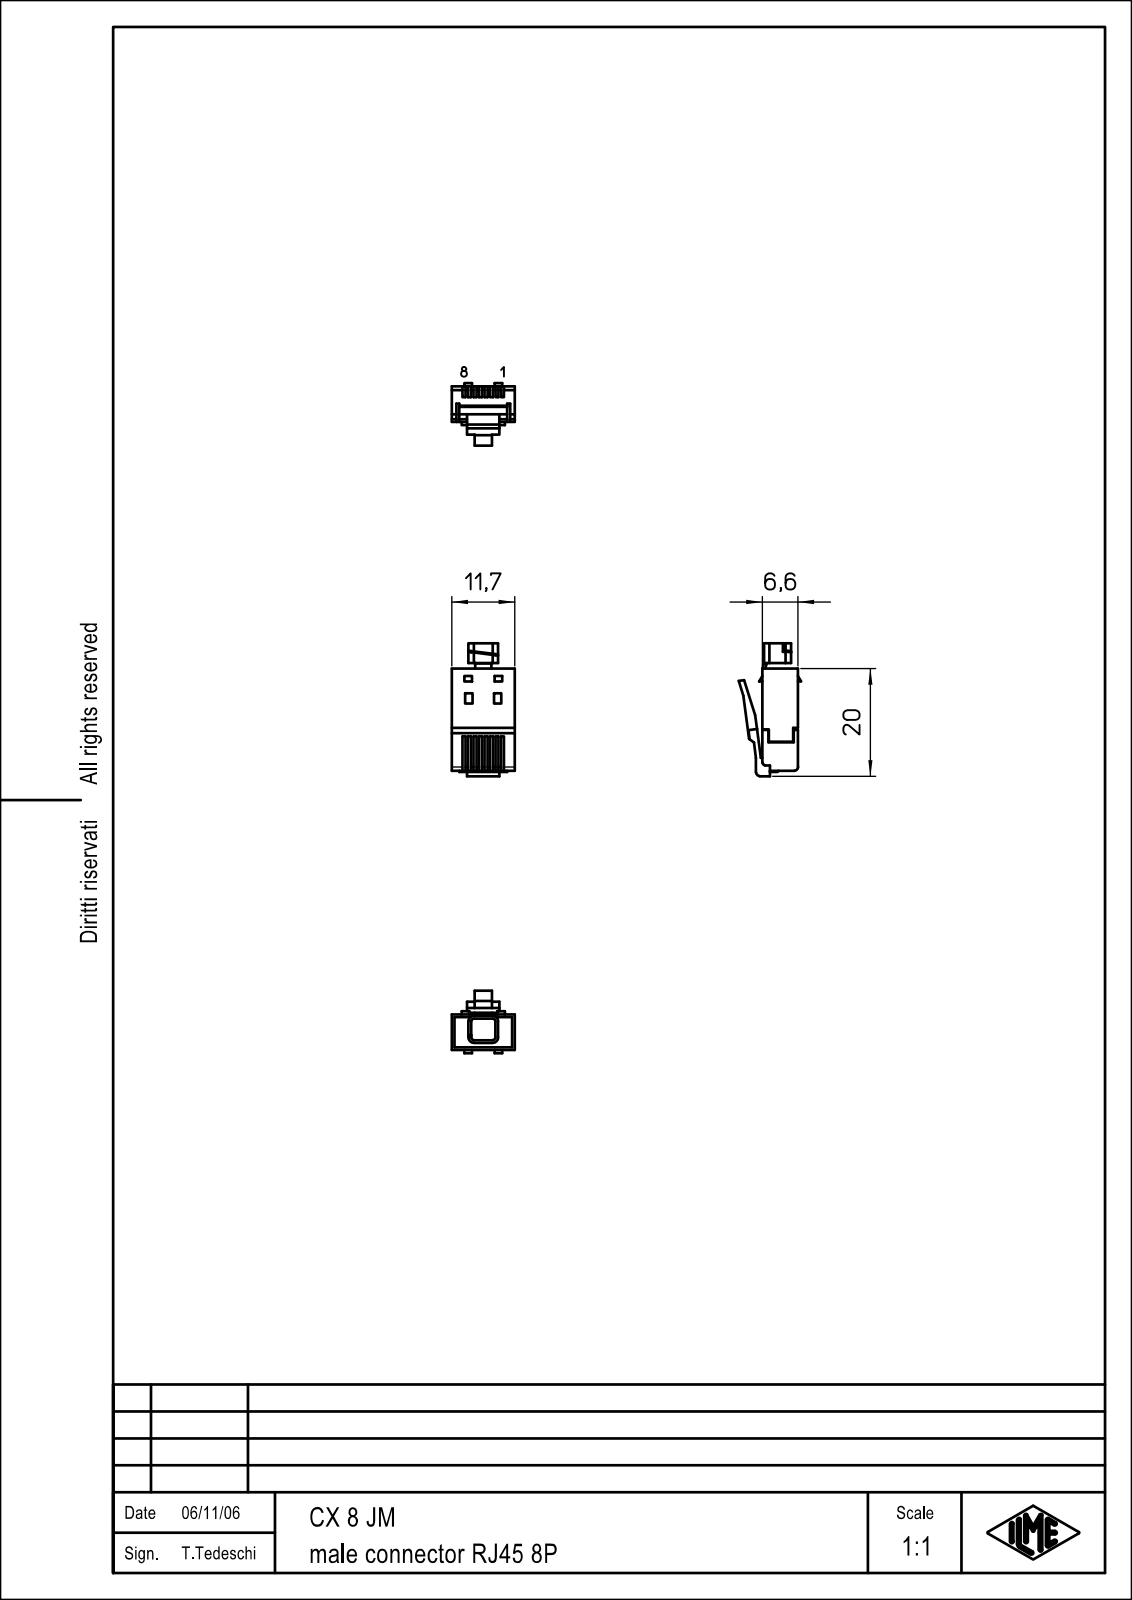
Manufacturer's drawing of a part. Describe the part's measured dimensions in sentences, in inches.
The part is named "CX_8_JM". Its 3-D file was written by "CoCreate Modeling 16.00A 16-Aug-2008 (C) Parametric Technology GmbH (AUTOMOTIVE_DESIGN)". It is 1 solid with 172 faces: 146 planar, 26 cylindrical and 0 other. Overall it measures 0.972 by 0.461 by 0.382 inches. Its volume is 0.082 cubic inches and its surface area 2.483 square inches. Partial cylindrical surfaces (rounded edges, fillets, slot ends): 5 of radius 0.02, 4 of radius 0.039, 2 of radius 0.028. The main face-to-face distances are 0.26, 0.02, 0.461, 0.079, 0.031, 0.067, 0.04, 0.055, 0.035, 0.08.
